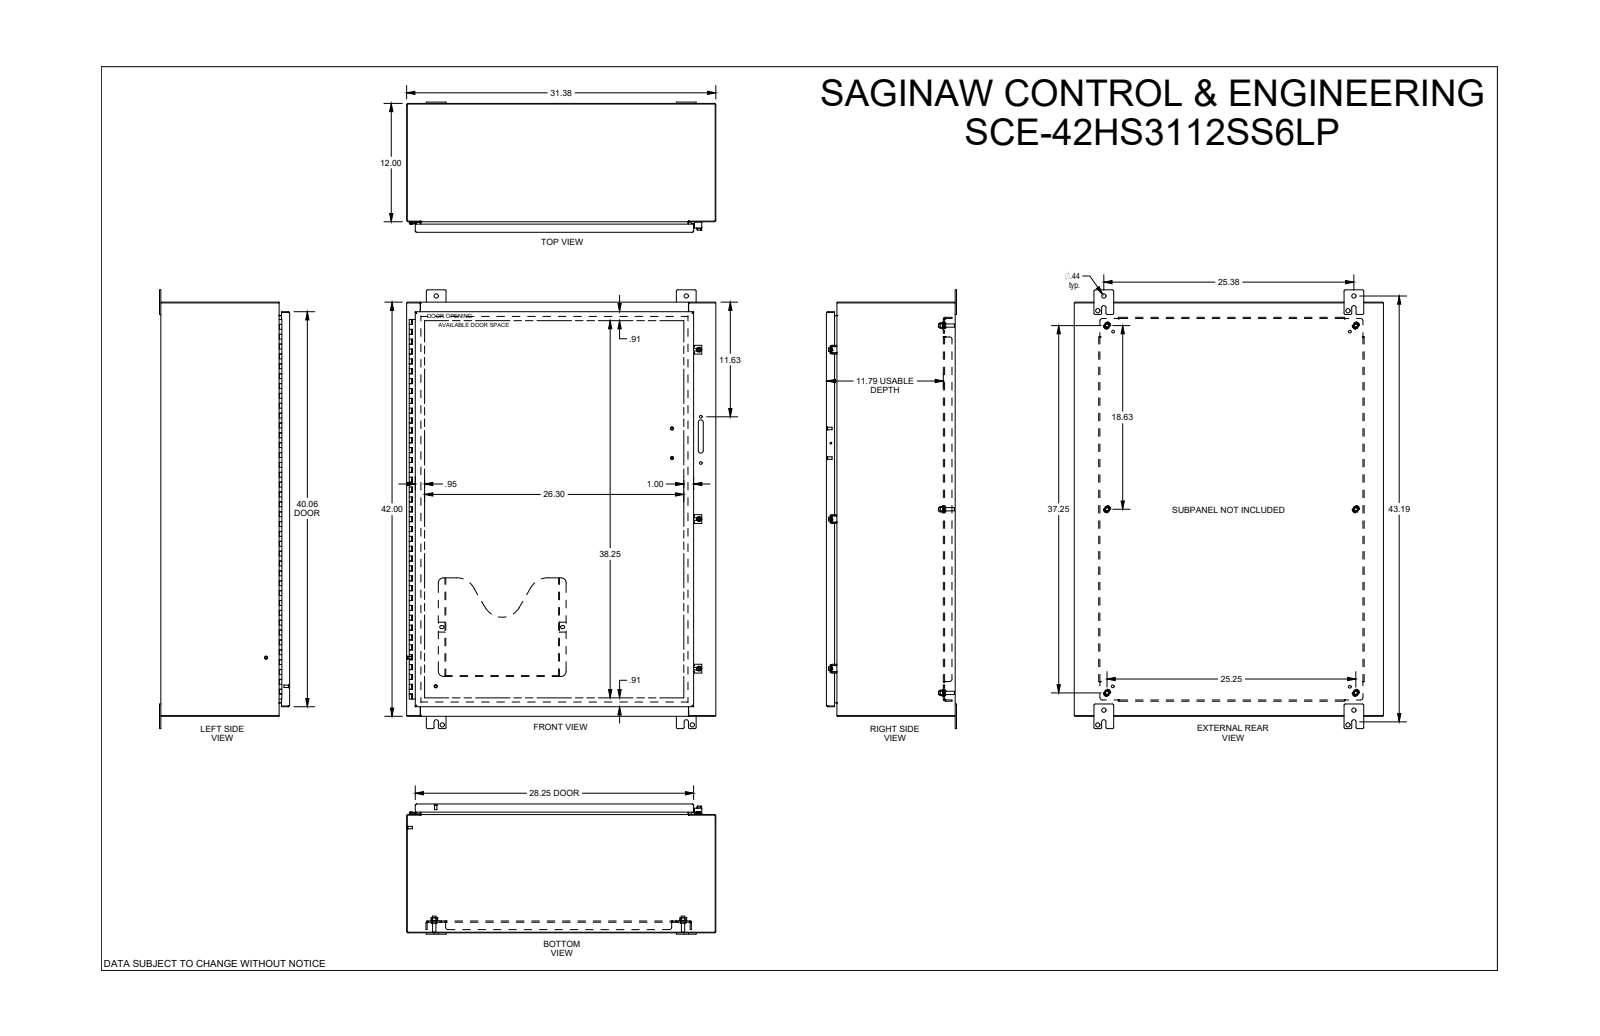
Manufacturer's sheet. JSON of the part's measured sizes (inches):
{"part_name": "SCE-42HS3112LP", "step_written_by": "SolidWorks 2021 (AUTOMOTIVE_DESIGN)", "units": "inches", "bodies": {"solids": 73, "faces": 3324, "planar": 1276, "cylindrical": 980, "other": 1068}, "overall_size": [44.5, 31.375, 13.343], "volume_in3": 534.7, "surface_area_in2": 12312, "round_holes": [[0.172, 6], [0.205, 6], [0.244, 6], [0.281, 6], [0.312, 6], [0.367, 6], [0.375, 6], [0.5, 6], [0.31, 4], [0.04, 3], [0.203, 3], [0.218, 3]], "round_bosses_or_shafts": [[0.25, 9], [0.248, 9], [0.17, 9], [0.366, 6], [0.332, 6], [0.24, 6], [0.59, 4], [0.376, 4]], "partial_cylinders_radius": [[0.01, 147], [0.025, 76], [0.015, 28], [0.185, 21], [0.04, 18], [0.029, 12], [0.043, 12], [0.06, 12]], "face_to_face_distances": [0.075, 12.993, 12.918, 13.068, 1.125, 1.2, 11.868, 11.793, 0.125, 1.075], "hole_center_spacings": [16.25, 40.5, 0.494, 0.875, 1.637, 2.282, 16.742, 18.625]}
